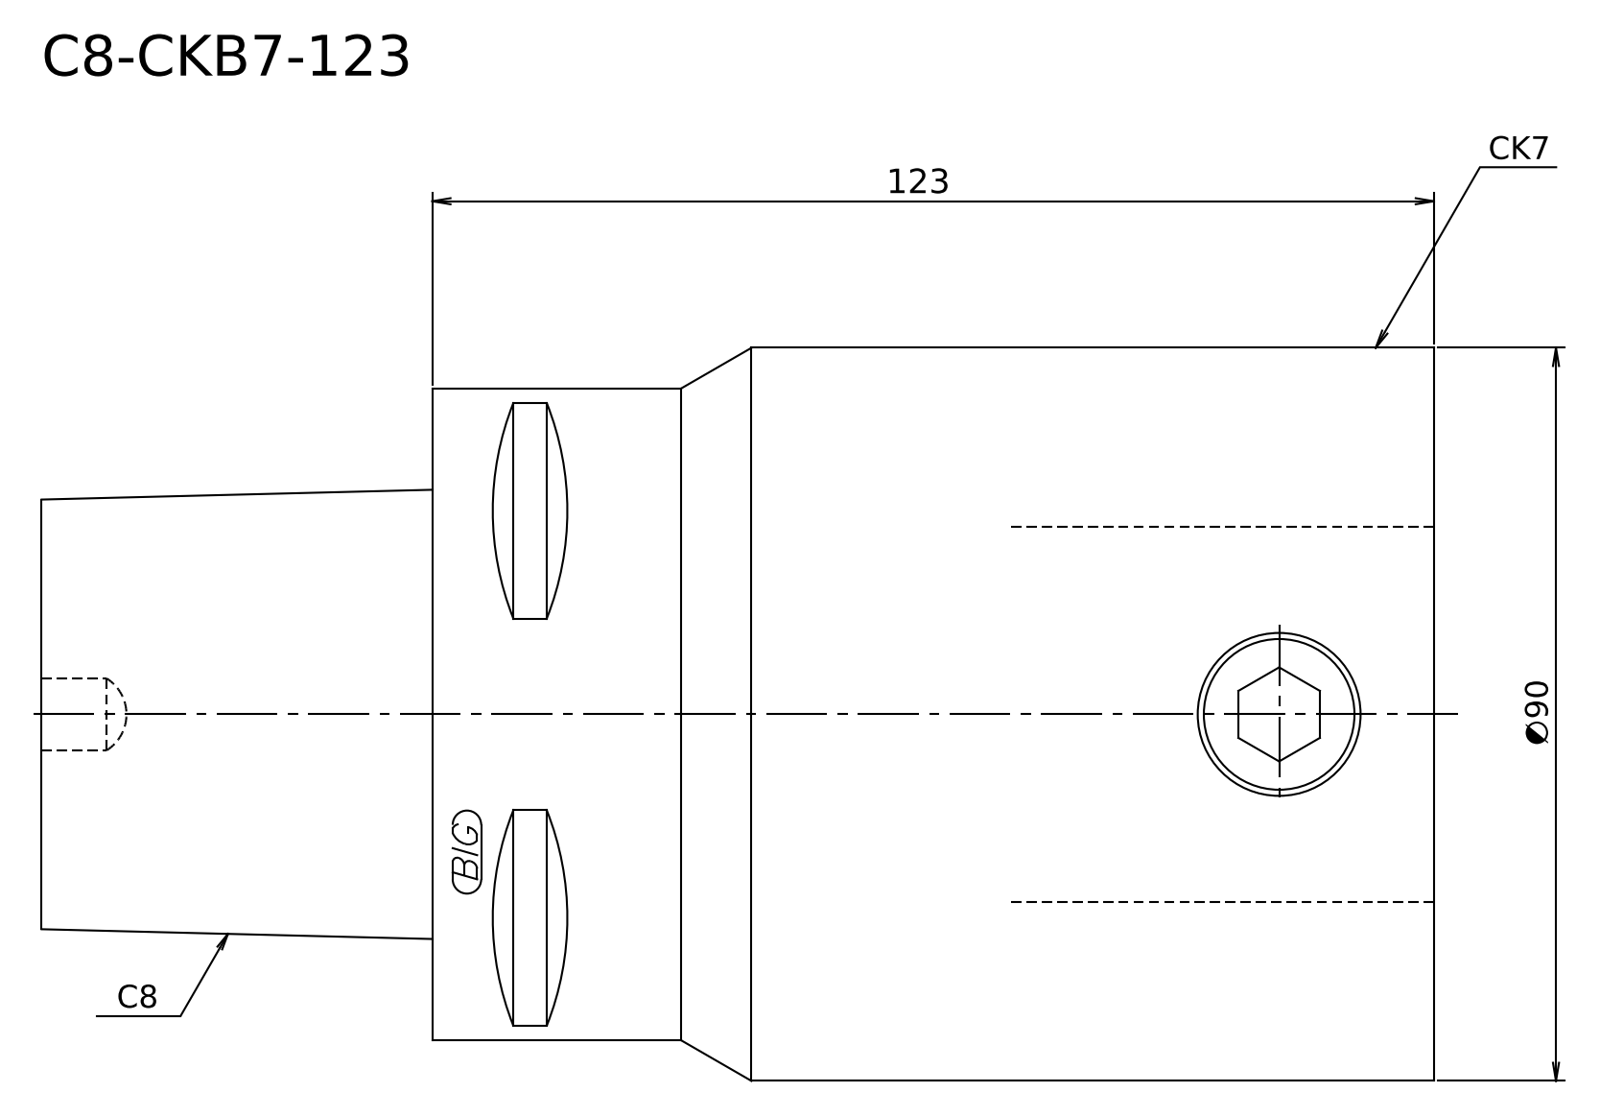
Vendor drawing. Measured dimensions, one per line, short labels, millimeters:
written by: Kubotek KeyCreator V8.5.1 (14335) (CONFIG_CONTROL_DESIGN)
unit: mm
bodies: 1 solid, 8 faces (3 planar, 2 cylindrical, 3 other)
size: 171 × 90 × 90
volume: 842 001 mm³; area: 53 350 mm²
bosses: 1× ⌀90, 1× ⌀79.98
face distances: 123, 171, 48
